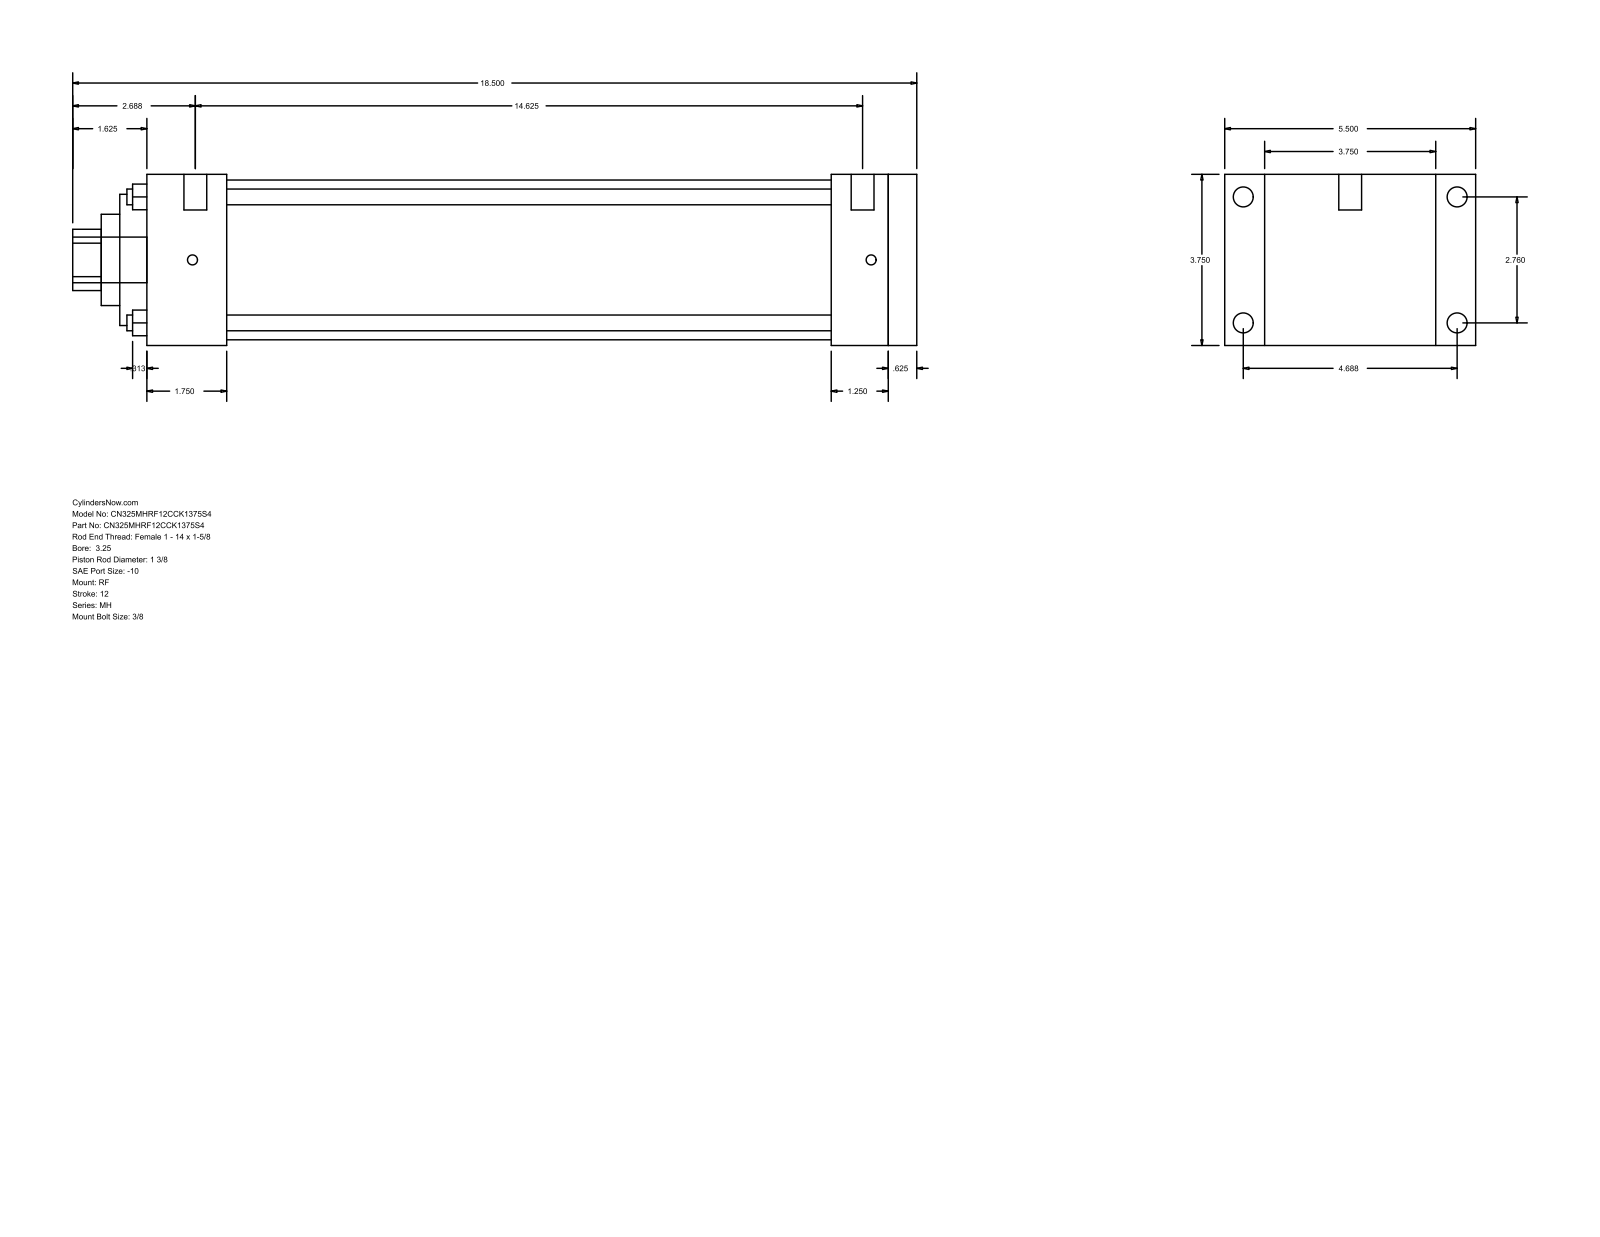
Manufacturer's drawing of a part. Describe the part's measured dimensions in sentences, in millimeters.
The part is named "MH_RF__0325_1.375". Its 3-D file was written by "GSSL Pune (CONFIG_CONTROL_DESIGN)". It is 0 solids with 94 faces: 65 planar, 29 cylindrical and 0 other. Overall it measures 469.9 by 139.7 by 95.25 millimeters. Round holes: 4 of diameter 8.76, 1 of diameter 34.92, 1 of diameter 50.8, 1 of diameter 73.03, 1 of diameter 88.9. Round bosses or shafts: 4 of diameter 11.13, 4 of diameter 5.56, 2 of diameter 12.7, 1 of diameter 25.4. Partial cylindrical surfaces (rounded edges, fillets, slot ends): 1 of radius 17.06. The main face-to-face distances are 95.24, 428.63, 15.88, 412.75, 22.23, 117.47, 44.45, 368.3, 384.18, 381. The hole center spacings are 49.57, 70.1, 99.14.
